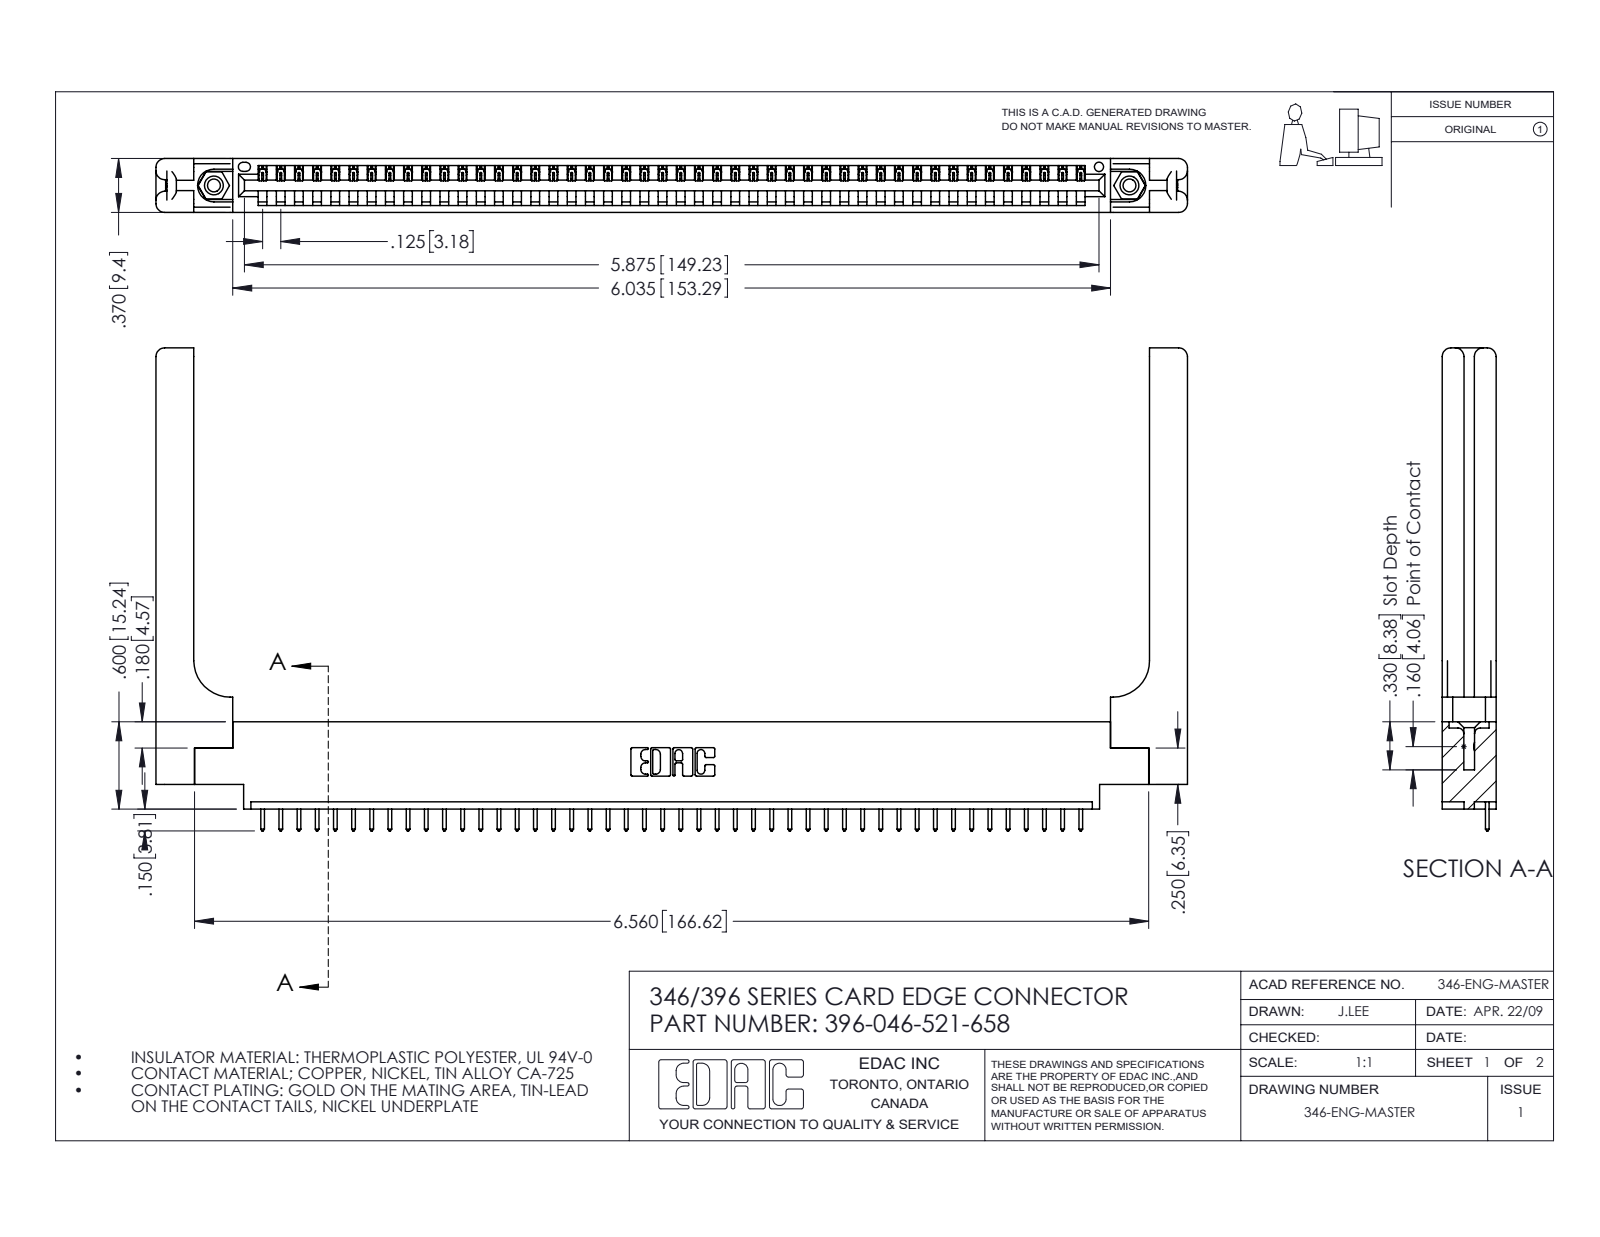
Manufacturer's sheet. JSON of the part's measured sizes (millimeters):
{"part_name": "396-046-521-658; 346 Part_0.170 Offset - 0.156 Dia-TH; 346-220-058_345-220-058; 345-250-001_345-250-001-102 (+1 more)", "step_written_by": "SolidWorks 2016 (CONFIG_CONTROL_DESIGN)", "units": "millimeters", "bodies": {"solids": 51, "faces": 3050, "planar": 2068, "cylindrical": 922, "other": 60}, "overall_size": [180.1, 84.3, 9.4], "volume_mm3": 24500, "surface_area_mm2": 26080, "round_holes": [[2.3, 2], [3.2, 2], [4, 2], [1.6, 1]], "round_bosses_or_shafts": [[3.9, 2]], "partial_cylinders_radius": [[0.2, 92], [0.3, 92], [0.3, 22], [1.5, 16], [0.2, 6], [0.8, 6], [0.7, 3], [0.8, 2]], "face_to_face_distances": [9.4, 1.2, 8.2, 1.8, 3.8, 3.8, 6.4, 7.6, 0.6, 5.6], "hole_center_spacings": [6.2, 154.6, 159.9]}
